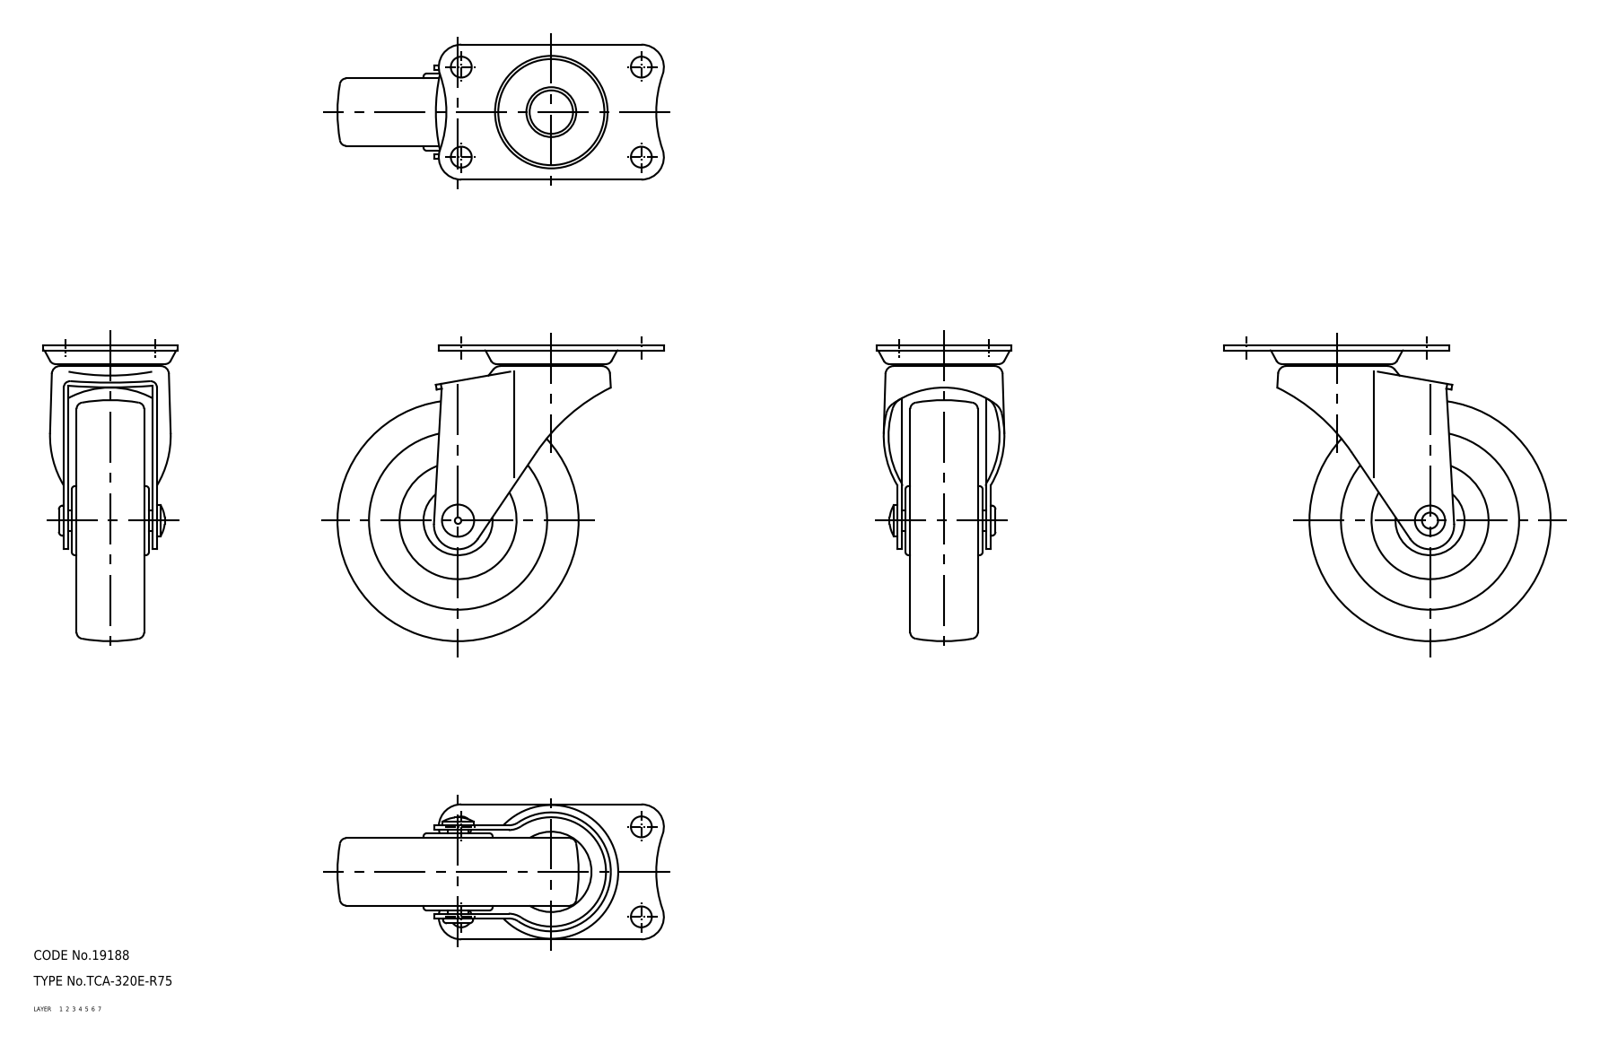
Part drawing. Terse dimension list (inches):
name: wheel; mounting plate; main shaft; axle (+1 more)
written by: CADfix (AUTOMOTIVE_DESIGN)
unit: in
bodies: 5 solids, 233 faces (0 planar, 0 cylindrical, 233 other)
size: 3.996 × 3.622 × 1.654
volume: 6.372 in³; area: 52.61 in²
